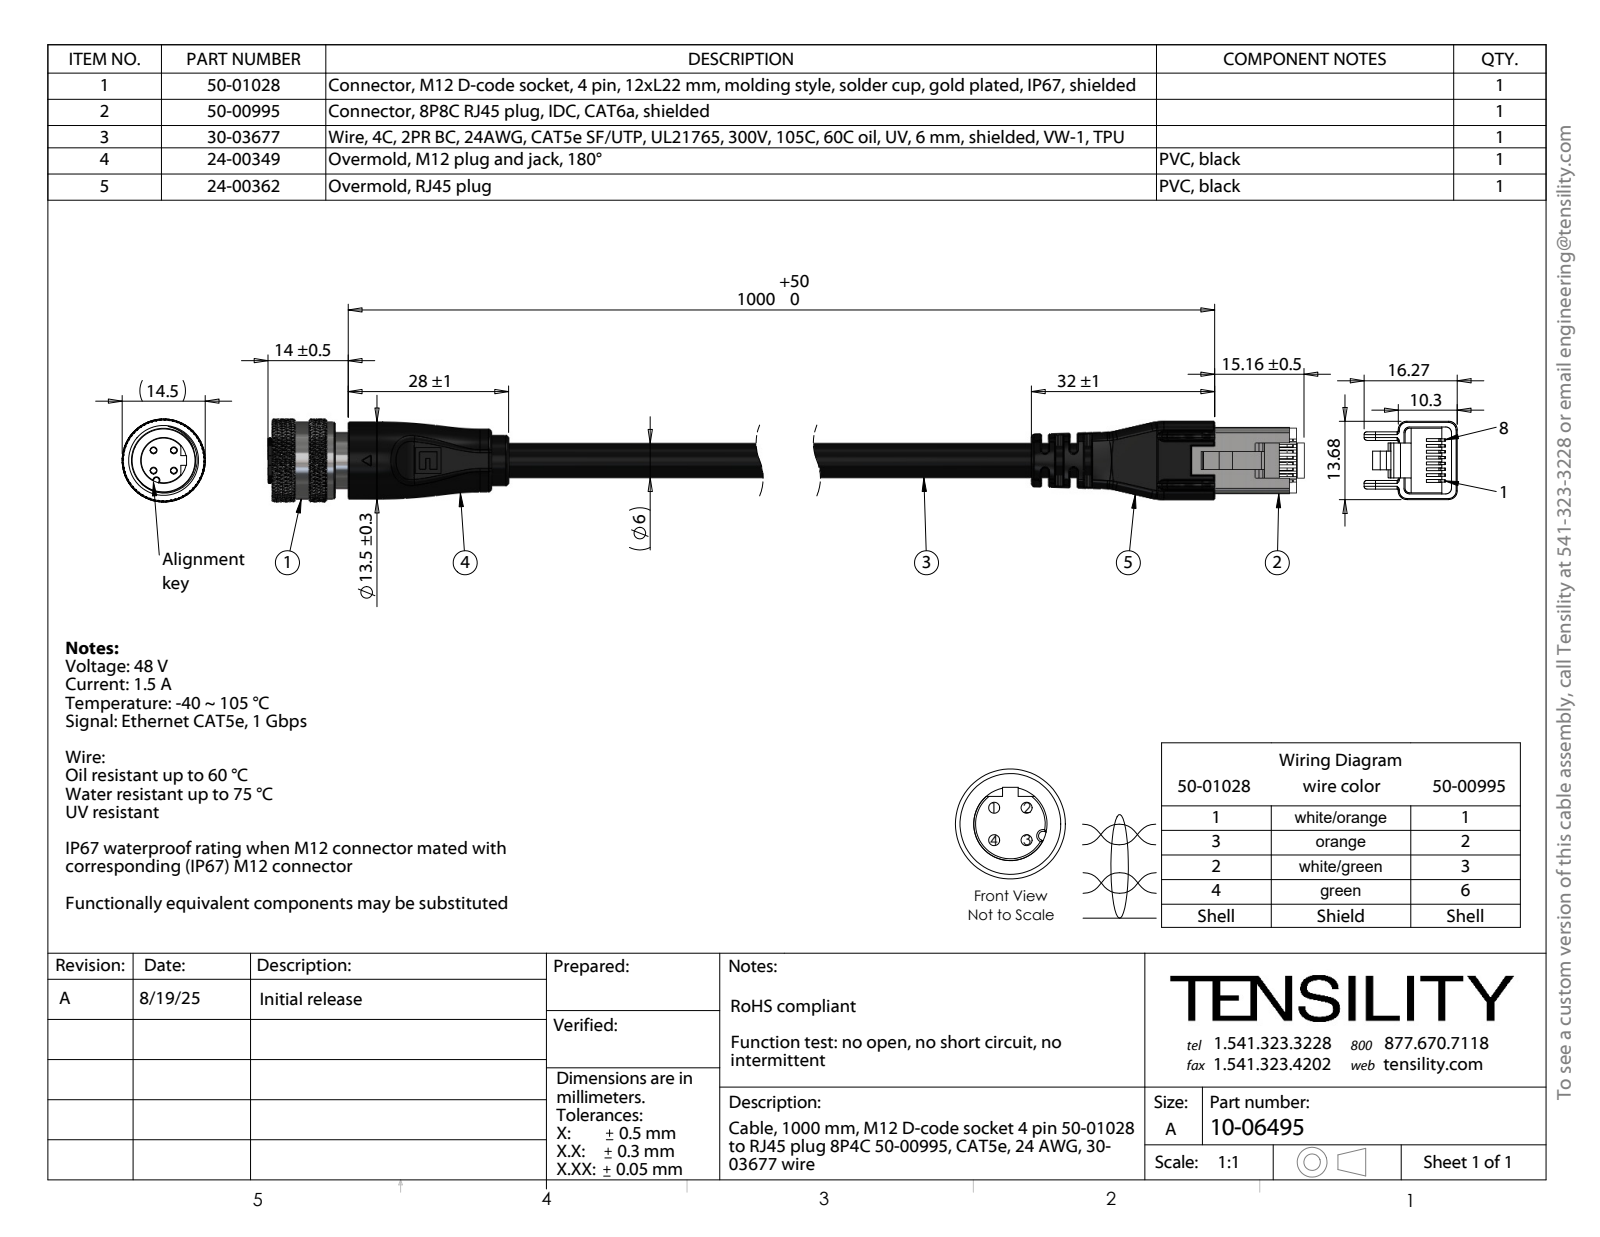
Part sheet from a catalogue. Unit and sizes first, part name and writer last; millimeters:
Units: millimetres
Overall size (bounding box): 229.11 × 18.37 × 14.5
Round holes (diameter × count): ⌀0.2 ×28, ⌀1.05 ×4, ⌀1.1 ×4, ⌀1.2 ×4, ⌀3.16 ×1, ⌀3.21 ×1, ⌀3.56 ×1, ⌀9 ×1, ⌀10 ×1, ⌀11.2 ×1
Round bosses / shafts (diameter × count): ⌀1.6 ×4, ⌀1.5 ×4, ⌀13.5 ×1, ⌀11 ×1, ⌀10.6 ×1, ⌀10.5 ×1, ⌀9.8 ×1, ⌀9.7 ×1
Partial cylindrical surfaces — rounded edges, fillets, slot ends (radius × count): R0.2 ×11, R0.1 ×10, R0.5 ×10, R1.5 ×10, R0.62 ×8, R0.4 ×6, R1 ×5, R10 ×4
Main face-to-face distances: 1.25, 1, 2.5, 3.75, 9.3, 5, 1.5, 199.5, 12.68, 8.5
Hole centre spacings: 1.91, 0.36, 2.09, 1.06, 0.89, 1.08, 1.24, 1.8
Volume: 14 248 mm³ · Surface area: 29 704 mm²
Bodies: 55 solids, 3967 faces (546 planar, 928 cylindrical, 2493 other)
Part name (STEP PRODUCT): 50-01028-04_默认; 24-00349_Mexico; 10-06495; 50-01028-02_默认 (+7 more)
STEP written by: SolidWorks 2025 (CONFIG_CONTROL_DESIGN)
